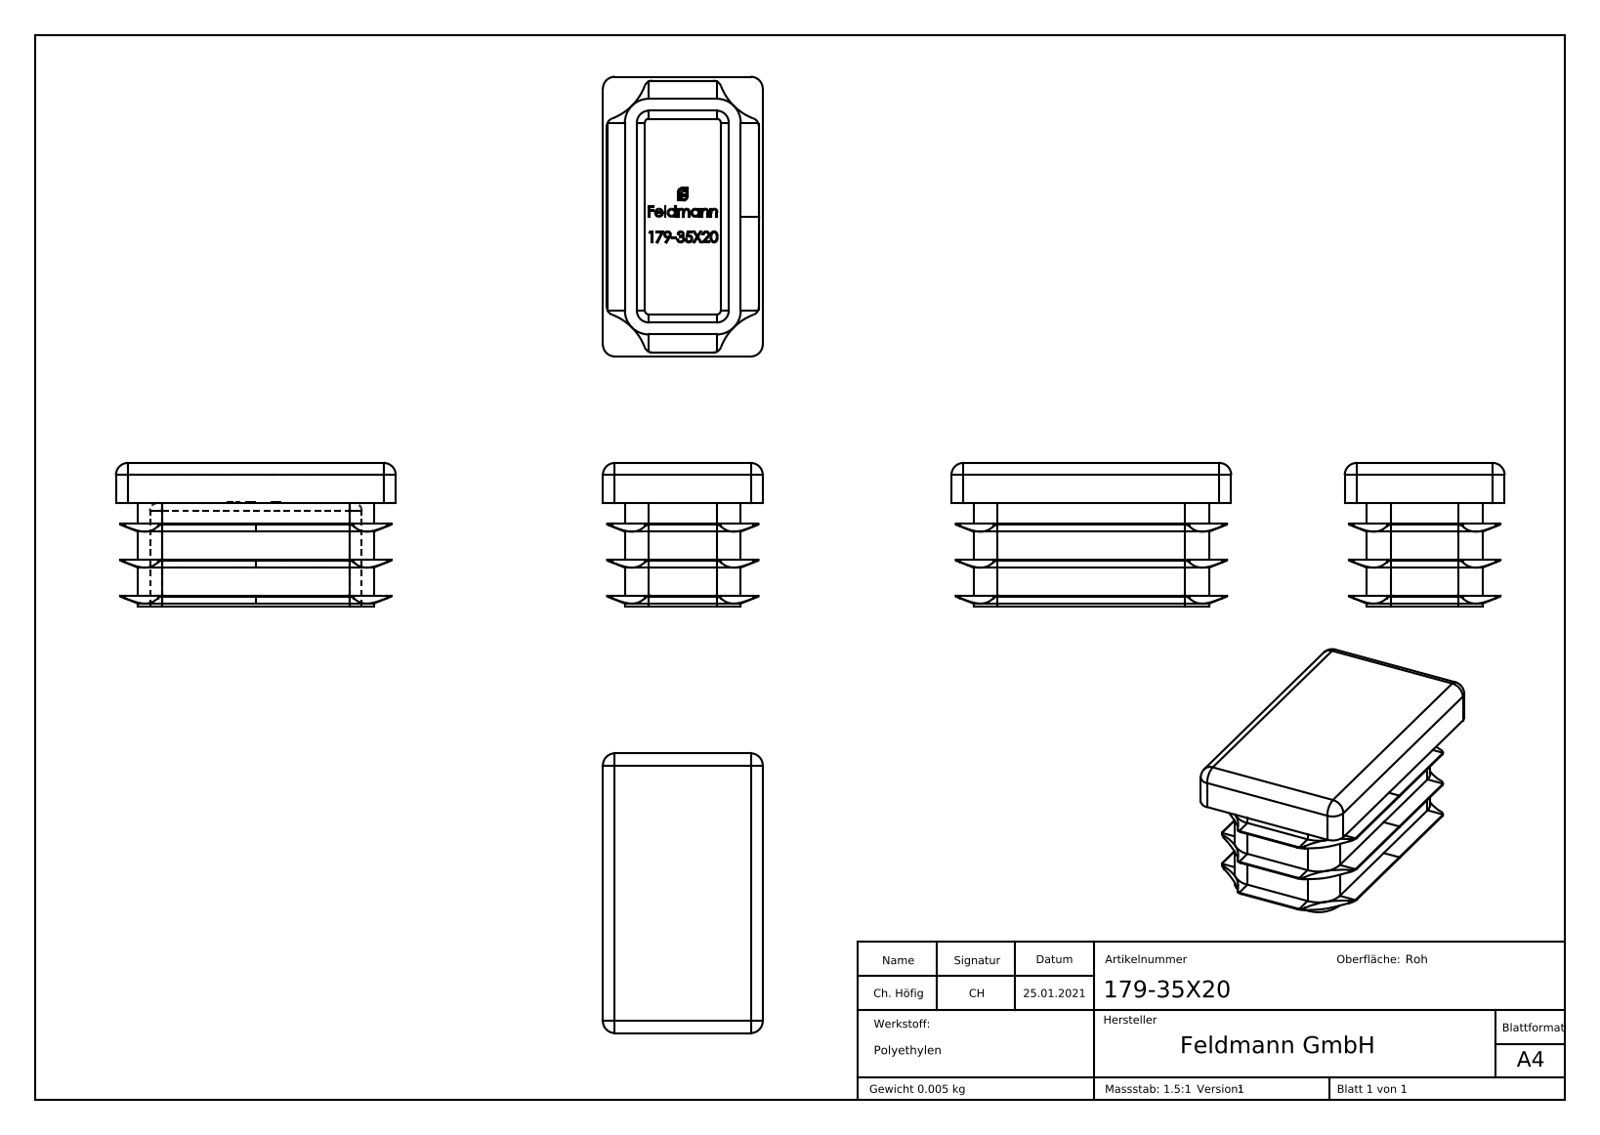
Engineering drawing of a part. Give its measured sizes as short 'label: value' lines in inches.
name: 179-35X20
written by: SolidWorks 2018 (CONFIG_CONTROL_DESIGN)
unit: in
bodies: 1 solid, 454 faces (225 planar, 83 cylindrical, 146 other)
size: 1.378 × 0.787 × 0.709
volume: 0.32 in³; area: 7.262 in²
rounds: 12× R0.039, 12× R0.059, 4× R0.118, 4× R0.276
face distances: 0.059, 0.512, 0.197, 0.108, 0.167, 0.177, 0.453, 0.571, 0.62, 0.679
